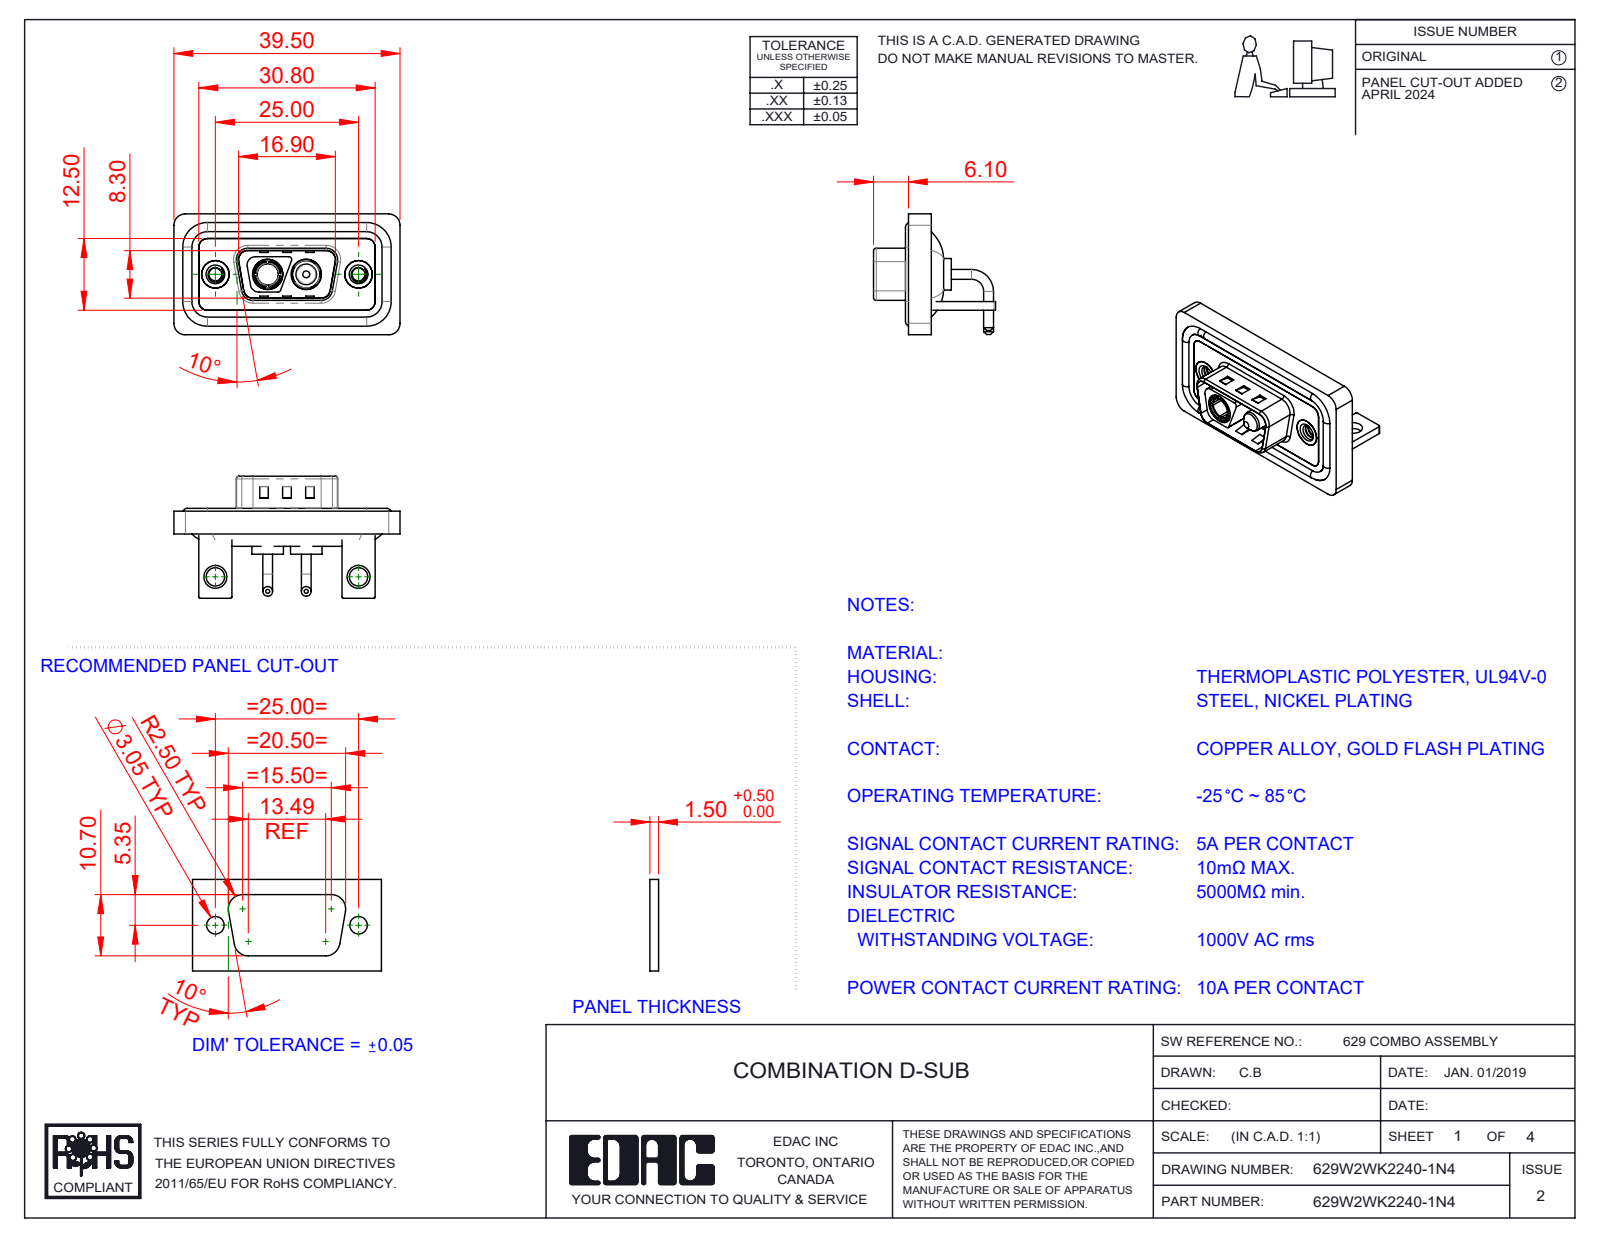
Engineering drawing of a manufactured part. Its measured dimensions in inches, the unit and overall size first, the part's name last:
Units: inches
Overall size (bounding box): 1.555 × 0.839 × 0.831
Round holes (diameter × count): ⌀0.089 ×2, ⌀0.126 ×2, ⌀0.157 ×2, ⌀0.189 ×2, ⌀0.191 ×2, ⌀0.197 ×2, ⌀0.209 ×2, ⌀0.146 ×1
Round bosses / shafts (diameter × count): ⌀0.067 ×4, ⌀0.063 ×4, ⌀0.217 ×2, ⌀0.205 ×2, ⌀0.193 ×2, ⌀0.187 ×2, ⌀0.148 ×2, ⌀0.195 ×1
Partial cylindrical surfaces — rounded edges, fillets, slot ends (radius × count): R0.059 ×20, R0.079 ×19, R0.01 ×16, R0.02 ×11, R0.063 ×8, R0.024 ×4, R0.026 ×4, R0.035 ×4
Main face-to-face distances: 0.016, 0.059, 0.114, 0.031, 0.043, 0.047, 0.083, 0.063, 0.146, 0.098
Hole centre spacings: 0.36, 0.624, 0.984, 0.265
Volume: 0.295 in³ · Surface area: 12.42 in²
Bodies: 13 solids, 582 faces (209 planar, 249 cylindrical, 124 other)
Part name (STEP PRODUCT): 629W2WK2240-1N4; 629Combo Stabilizer Bracket; Power Socket_10A RA; 629Combo Shell Rear_09 Contacts (+5 more)
STEP written by: SolidWorks 2023 (CONFIG_CONTROL_DESIGN)
